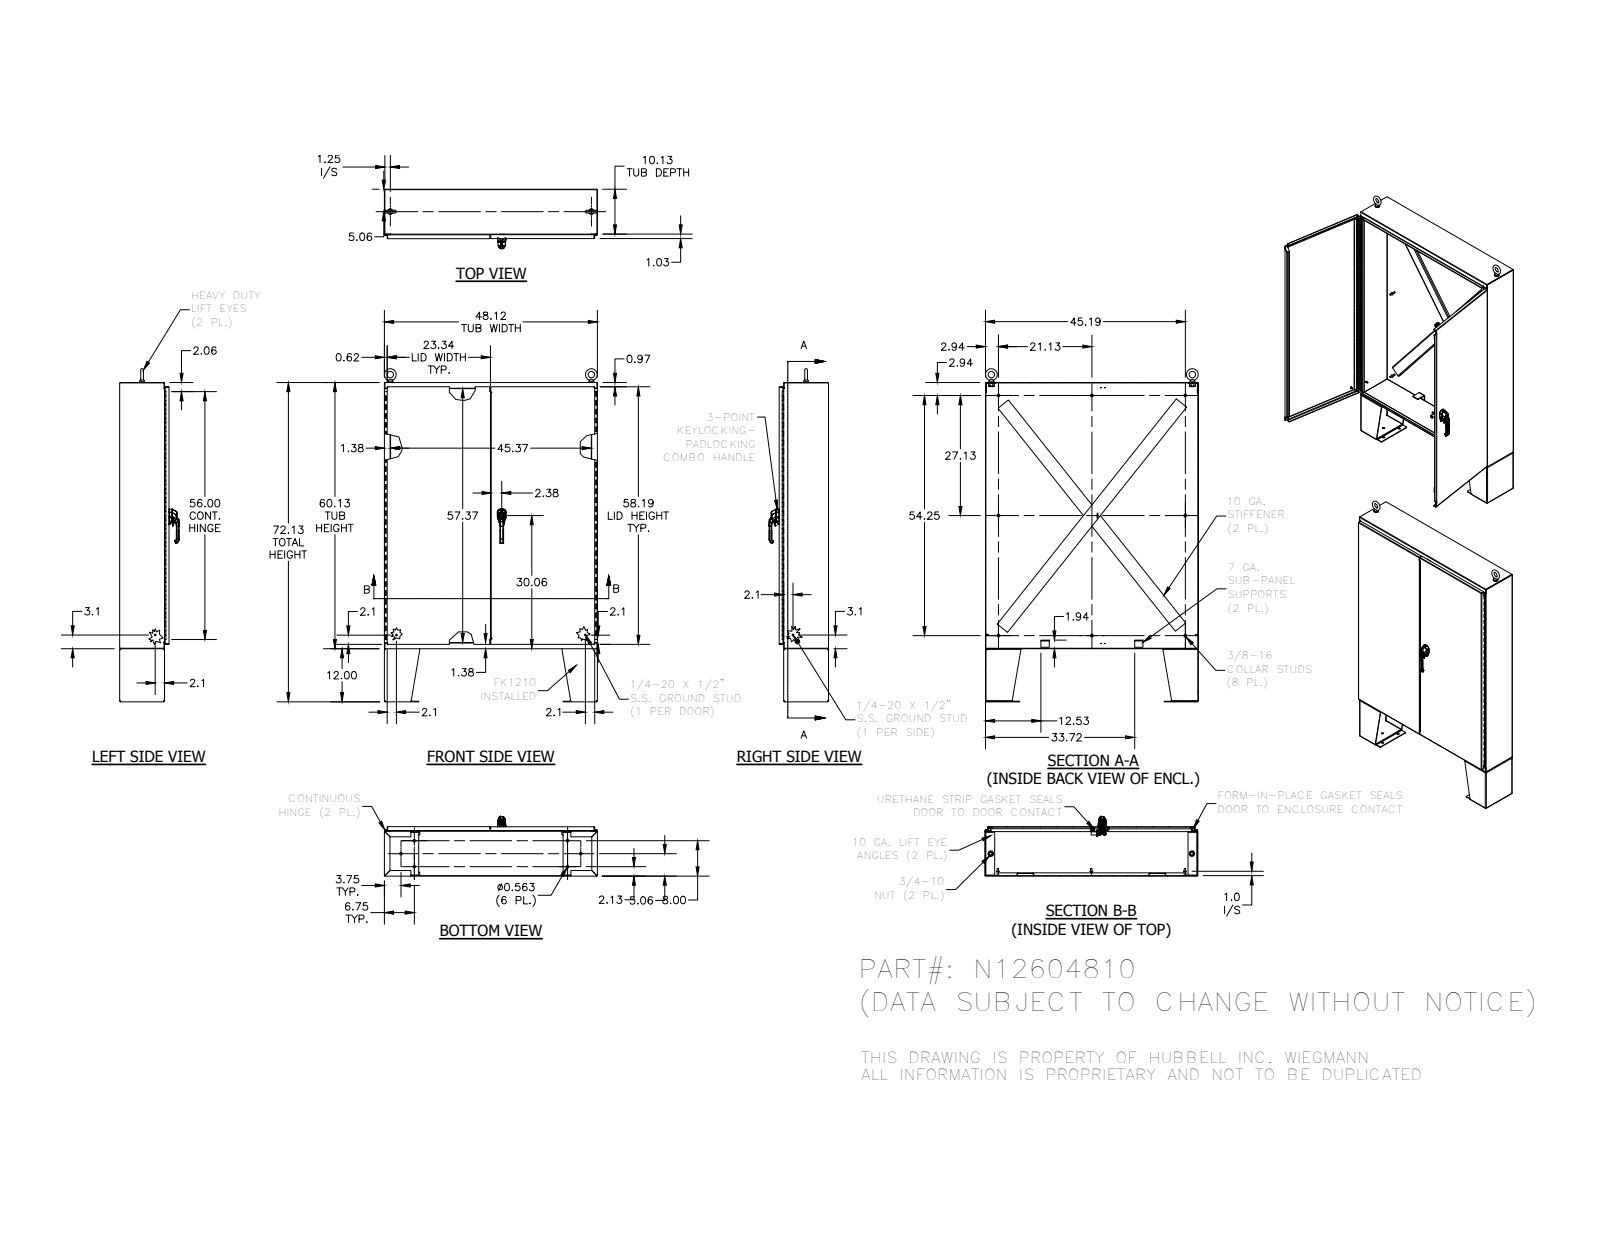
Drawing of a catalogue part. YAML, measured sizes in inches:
part_name: "N12604810"
step_written_by: "SolidWorks 2018 (AUTOMOTIVE_DESIGN)"
units: inches
bodies: {solids: 74, faces: 2388, planar: 1376, cylindrical: 712, other: 300}
overall_size: [75.248, 48.125, 13.33]
volume: 1079
surface_area: 21474
round_holes:
  - {diameter: 0.563, count: 18}
  - {diameter: 0.277, count: 8}
  - {diameter: 0.2, count: 4}
  - {diameter: 0.125, count: 3}
  - {diameter: 0.28, count: 3}
  - {diameter: 0.241, count: 2}
  - {diameter: 0.25, count: 2}
  - {diameter: 0.252, count: 2}
  - {diameter: 0.4, count: 2}
  - {diameter: 0.45, count: 2}
  - {diameter: 0.642, count: 2}
  - {diameter: 0.813, count: 2}
round_bosses_or_shafts:
  - {diameter: 0.33, count: 8}
  - {diameter: 0.25, count: 5}
  - {diameter: 0.625, count: 4}
  - {diameter: 0.625, count: 4}
  - {diameter: 0.337, count: 3}
  - {diameter: 1.25, count: 2}
  - {diameter: 1.12, count: 2}
  - {diameter: 1, count: 2}
partial_cylinders:
  - {radius: 0.031, count: 28}
  - {radius: 0.094, count: 23}
  - {radius: 0.219, count: 22}
  - {radius: 0.125, count: 19}
  - {radius: 0.05, count: 18}
  - {radius: 0.025, count: 16}
  - {radius: 0.03, count: 13}
  - {radius: 0.067, count: 8}
face_to_face_distances: [0.094, 11.058, 11.067, 10.965, 10.973, 11.152, 0.085, 11.16, 0.102, 60.031]
hole_center_spacings: [2.041, 4.198, 5, 6.064, 6.503, 8.356, 8.75, 9.566]
